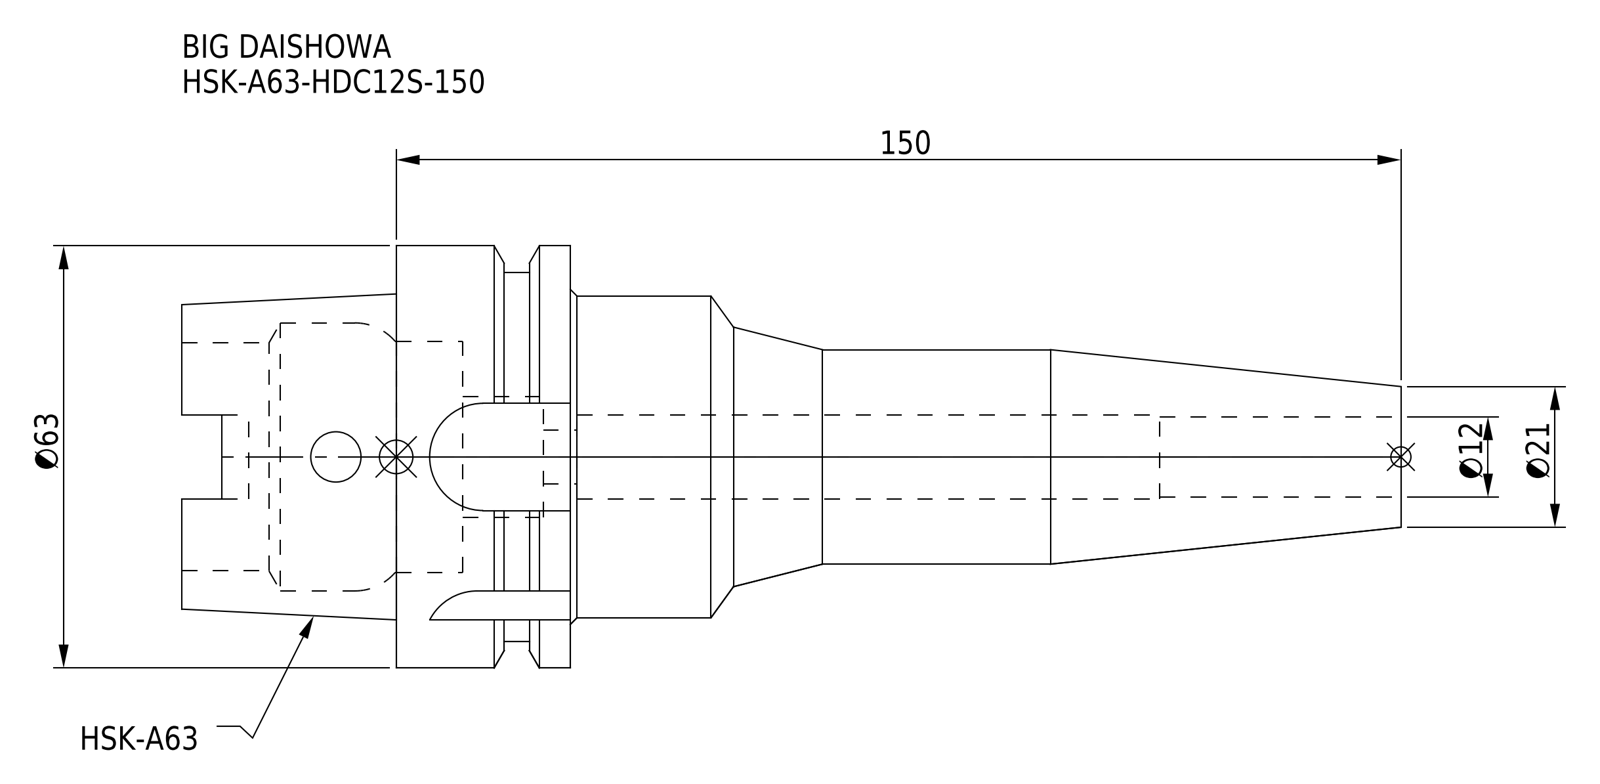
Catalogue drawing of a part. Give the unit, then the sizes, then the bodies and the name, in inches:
Units: inches
Overall size (bounding box): 7.165 × 2.48 × 2.48
Round holes (diameter × count): ⌀0.295 ×1, ⌀0.315 ×1, ⌀0.472 ×1, ⌀0.492 ×1, ⌀0.709 ×1, ⌀1.339 ×1, ⌀1.358 ×1, ⌀1.575 ×1
Round bosses / shafts (diameter × count): ⌀2.48 ×1, ⌀2.165 ×1, ⌀1.89 ×1, ⌀1.26 ×1
Partial cylindrical surfaces — rounded edges, fillets, slot ends (radius × count): R0.113 ×4, R0.315 ×4
Main face-to-face distances: 1.024, 0.632, 0.392, 2.283, 1.652, 1.26, 2.087, 0.472, 4.882, 5.514
Volume: 10.96 in³ · Surface area: 60.23 in²
Bodies: 1 solid, 99 faces (38 planar, 39 cylindrical, 22 other)
Part name (STEP PRODUCT): HSK-A63-HDC12S-150
STEP written by: CREO PARAMETRIC BY PTC INC, 2016380 (AUTOMOTIVE_DESIGN)
